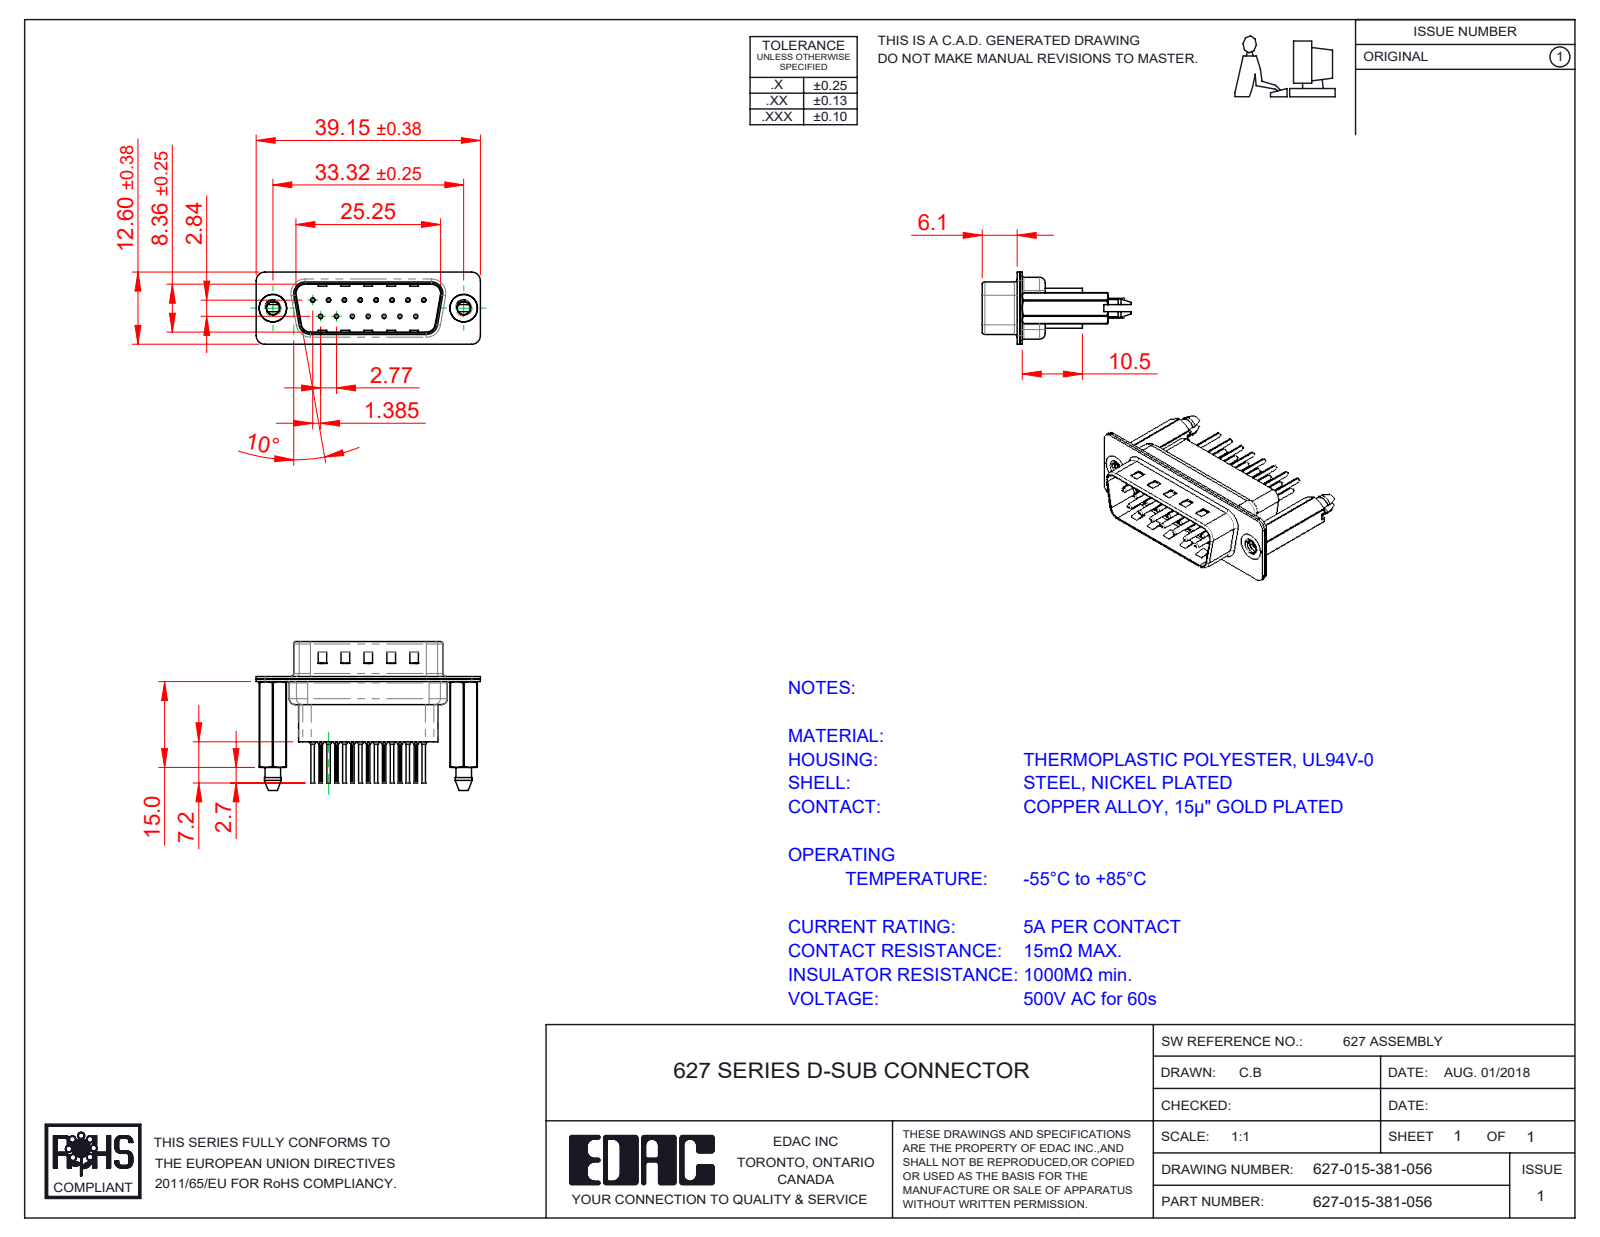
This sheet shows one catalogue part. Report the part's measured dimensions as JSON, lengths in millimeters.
{"part_name": "627 Shell Rear_15 Contacts; 627-015-381-056; 627 Contact Row 1_61; 627 Contact Row 2_61 (+3 more)", "step_written_by": "SolidWorks 2020 (CONFIG_CONTROL_DESIGN)", "units": "millimeters", "bodies": {"solids": 20, "faces": 1918, "planar": 531, "cylindrical": 754, "other": 633}, "overall_size": [39.15, 25.9, 12.6], "volume_mm3": 2936, "surface_area_mm2": 7555, "round_holes": [[0.2, 15], [0.35, 15], [1.1, 15], [1.6, 15], [2.26, 2], [4, 2], [4.8, 2]], "round_bosses_or_shafts": [[2, 15], [1.5, 15], [0.75, 15], [0.6, 15], [4.9, 2]], "partial_cylinders_radius": [[0.1, 30], [1.5, 18], [2, 12], [1.6, 10], [0.5, 8], [0.25, 4], [0.6, 4], [0.65, 4]], "face_to_face_distances": [0.4, 0.45, 0.9, 0.82, 9.58, 4.76, 1.5, 0.68, 7.68, 1.4], "hole_center_spacings": [3.16, 2.77, 5.54, 8.31, 11.08, 5.03, 5.04, 7.48]}
